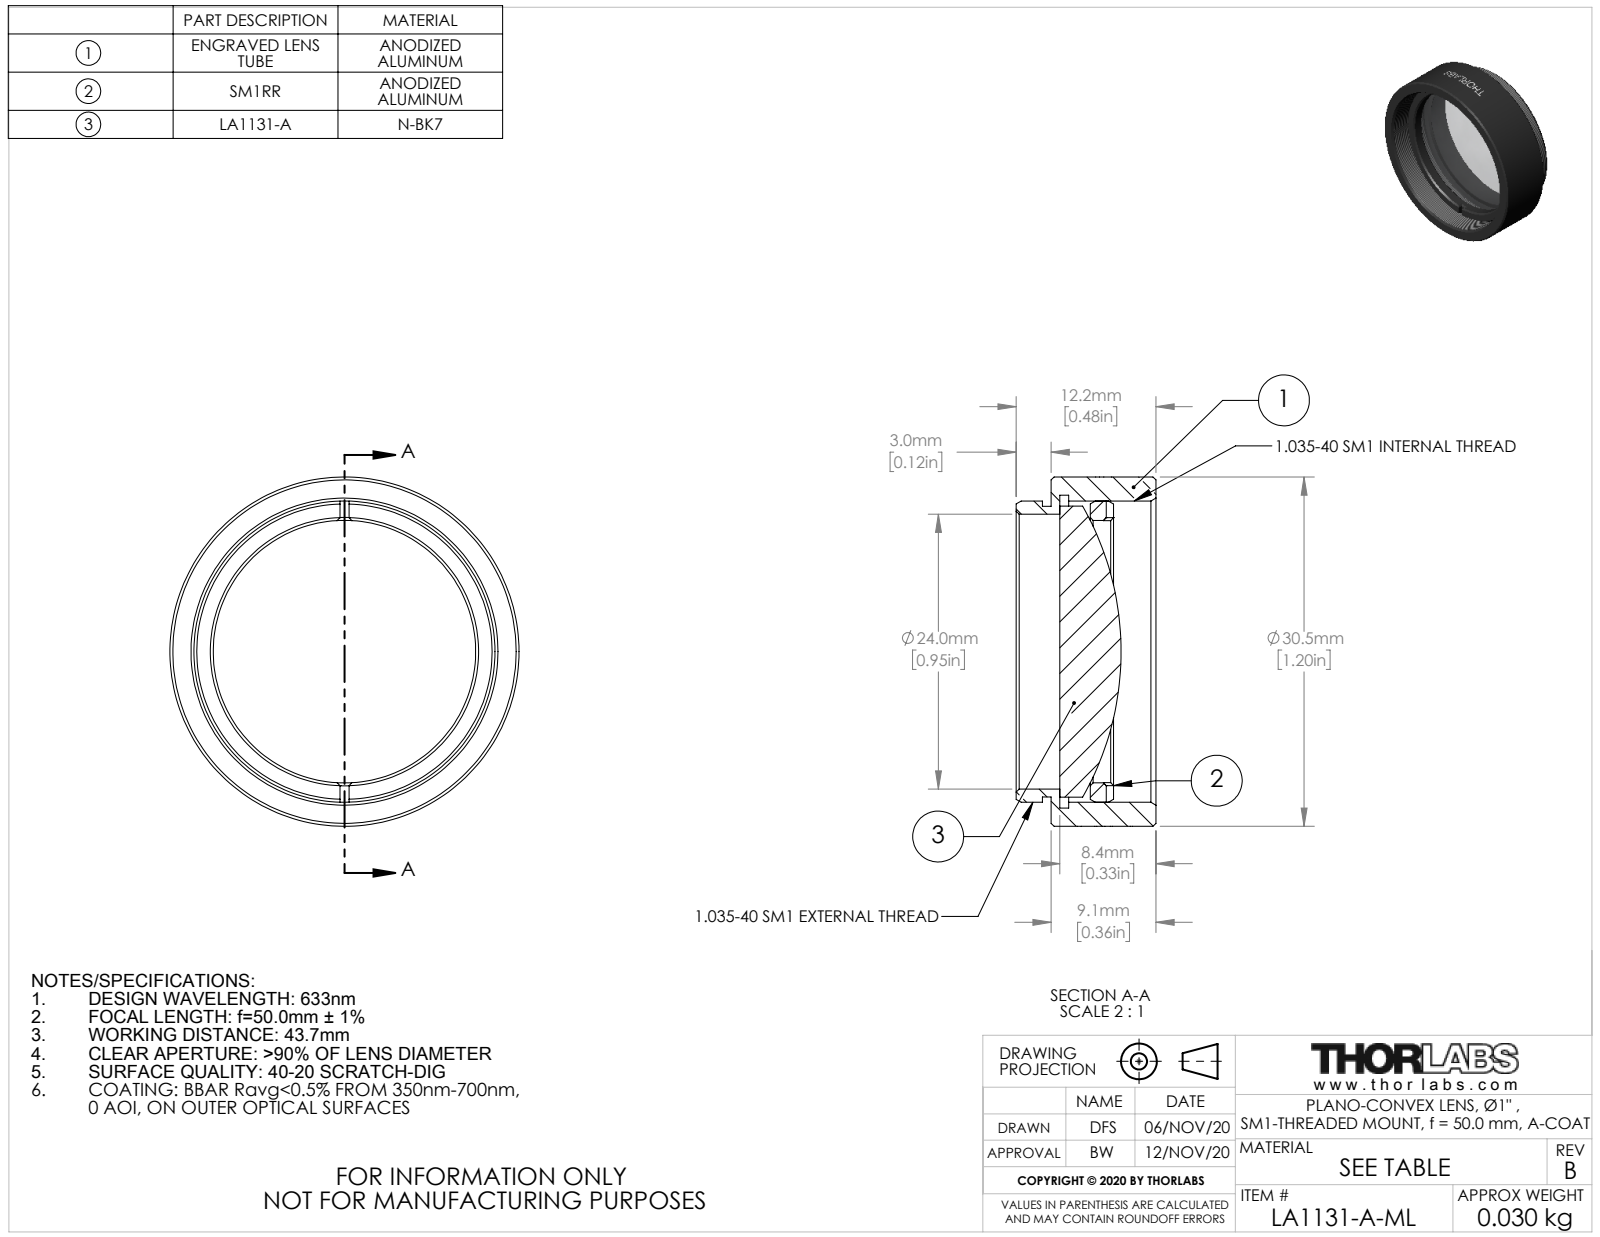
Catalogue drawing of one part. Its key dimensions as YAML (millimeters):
part_name: "24419-E0W"
step_written_by: "SolidWorks 2018 (CONFIG_CONTROL_DESIGN)"
units: millimeters
bodies: {solids: 3, faces: 147, planar: 20, cylindrical: 103, other: 24}
overall_size: [30.48, 30.48, 12.19]
volume: 4101
surface_area: 4483
round_holes:
  - {diameter: 22.91, count: 1}
  - {diameter: 24, count: 1}
  - {diameter: 26.29, count: 1}
  - {diameter: 27.3, count: 1}
round_bosses_or_shafts:
  - {diameter: 30.48, count: 1}
  - {diameter: 26.29, count: 1}
  - {diameter: 25.4, count: 1}
  - {diameter: 25.37, count: 1}
face_to_face_distances: [0.76, 9.15, 8.39, 3.42, 2.66, 5.73, 5.45, 4.69, 2.03, 3.7]
